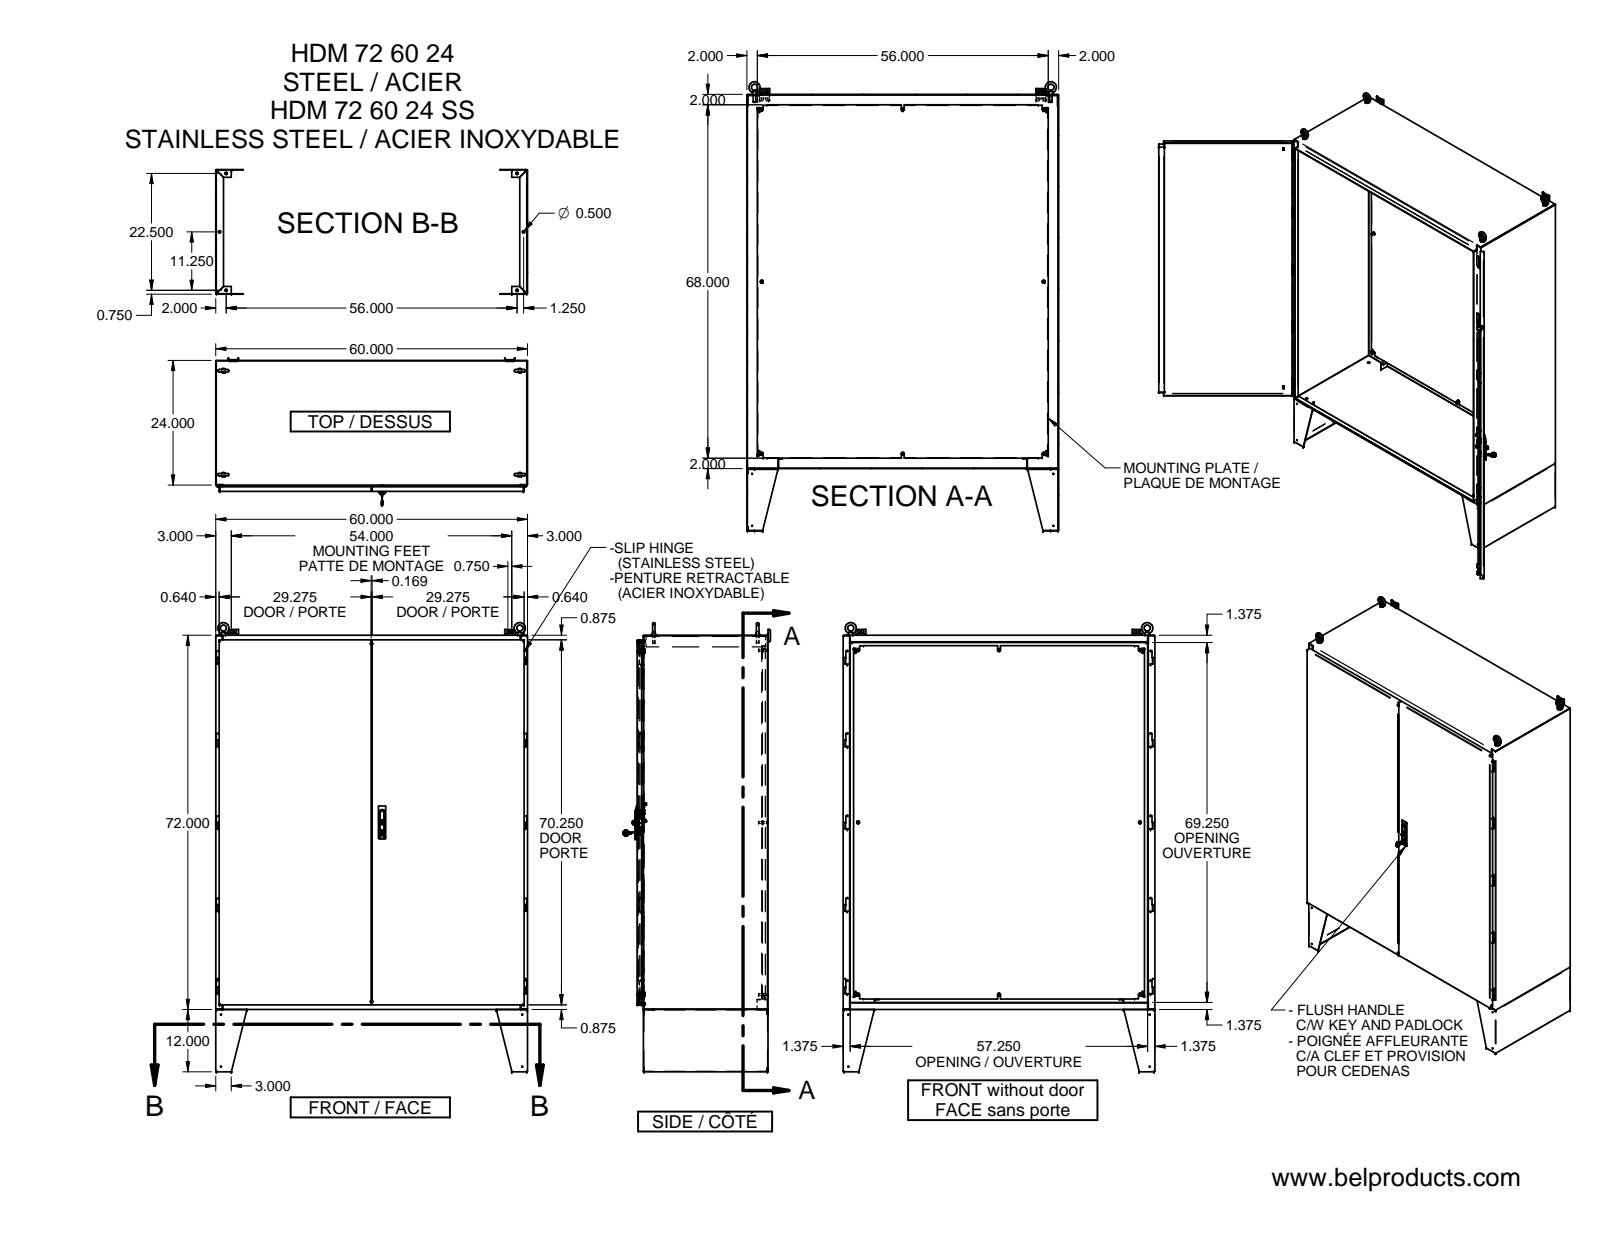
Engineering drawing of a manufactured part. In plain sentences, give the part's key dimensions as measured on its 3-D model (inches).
The part is named "POIGNÉE EMKA ASSEMBLÉE DROITE; ADAPTEUR_TIGE; HD726024_12GA_12_MCX; HD7260xxFOND_12GA (+8 more)". Its 3-D file was written by "Unknown (AUTOMOTIVE_DESIGN)". It is 59 solids with 3912 faces: 2410 planar, 684 cylindrical and 818 other. Overall it measures 86.449 by 60 by 25.647 inches. Its volume is 2 196 cubic inches and its surface area 42 070 square inches. Round holes: 40 of diameter 0.124, 18 of diameter 0.5, 16 of diameter 0.125, 4 of diameter 0.014, 4 of diameter 0.201, 4 of diameter 0.236, 4 of diameter 0.281, 4 of diameter 0.456, 4 of diameter 0.625, 4 of diameter 0.75, 2 of diameter 0.169, 2 of diameter 0.177. Round bosses or shafts: 40 of diameter 0.125, 16 of diameter 0.119, 8 of diameter 0.637, 8 of diameter 0.375, 8 of diameter 0.353, 8 of diameter 0.031, 4 of diameter 0.895, 4 of diameter 0.591. Partial cylindrical surfaces (rounded edges, fillets, slot ends): 42 of radius 0.032, 34 of radius 0.137, 25 of radius 0.063, 24 of radius 0.059, 18 of radius 0.118, 8 of radius 0.112, 8 of radius 0.228, 6 of radius 0.281. The main face-to-face distances are 0.105, 25.107, 24.006, 1.101, 25.002, 25.212, 59.895, 24.111, 0.996, 23.901. The hole center spacings are 15.856, 15.855, 2.703, 2.703, 31.711, 13.153, 15.856, 18.559.
